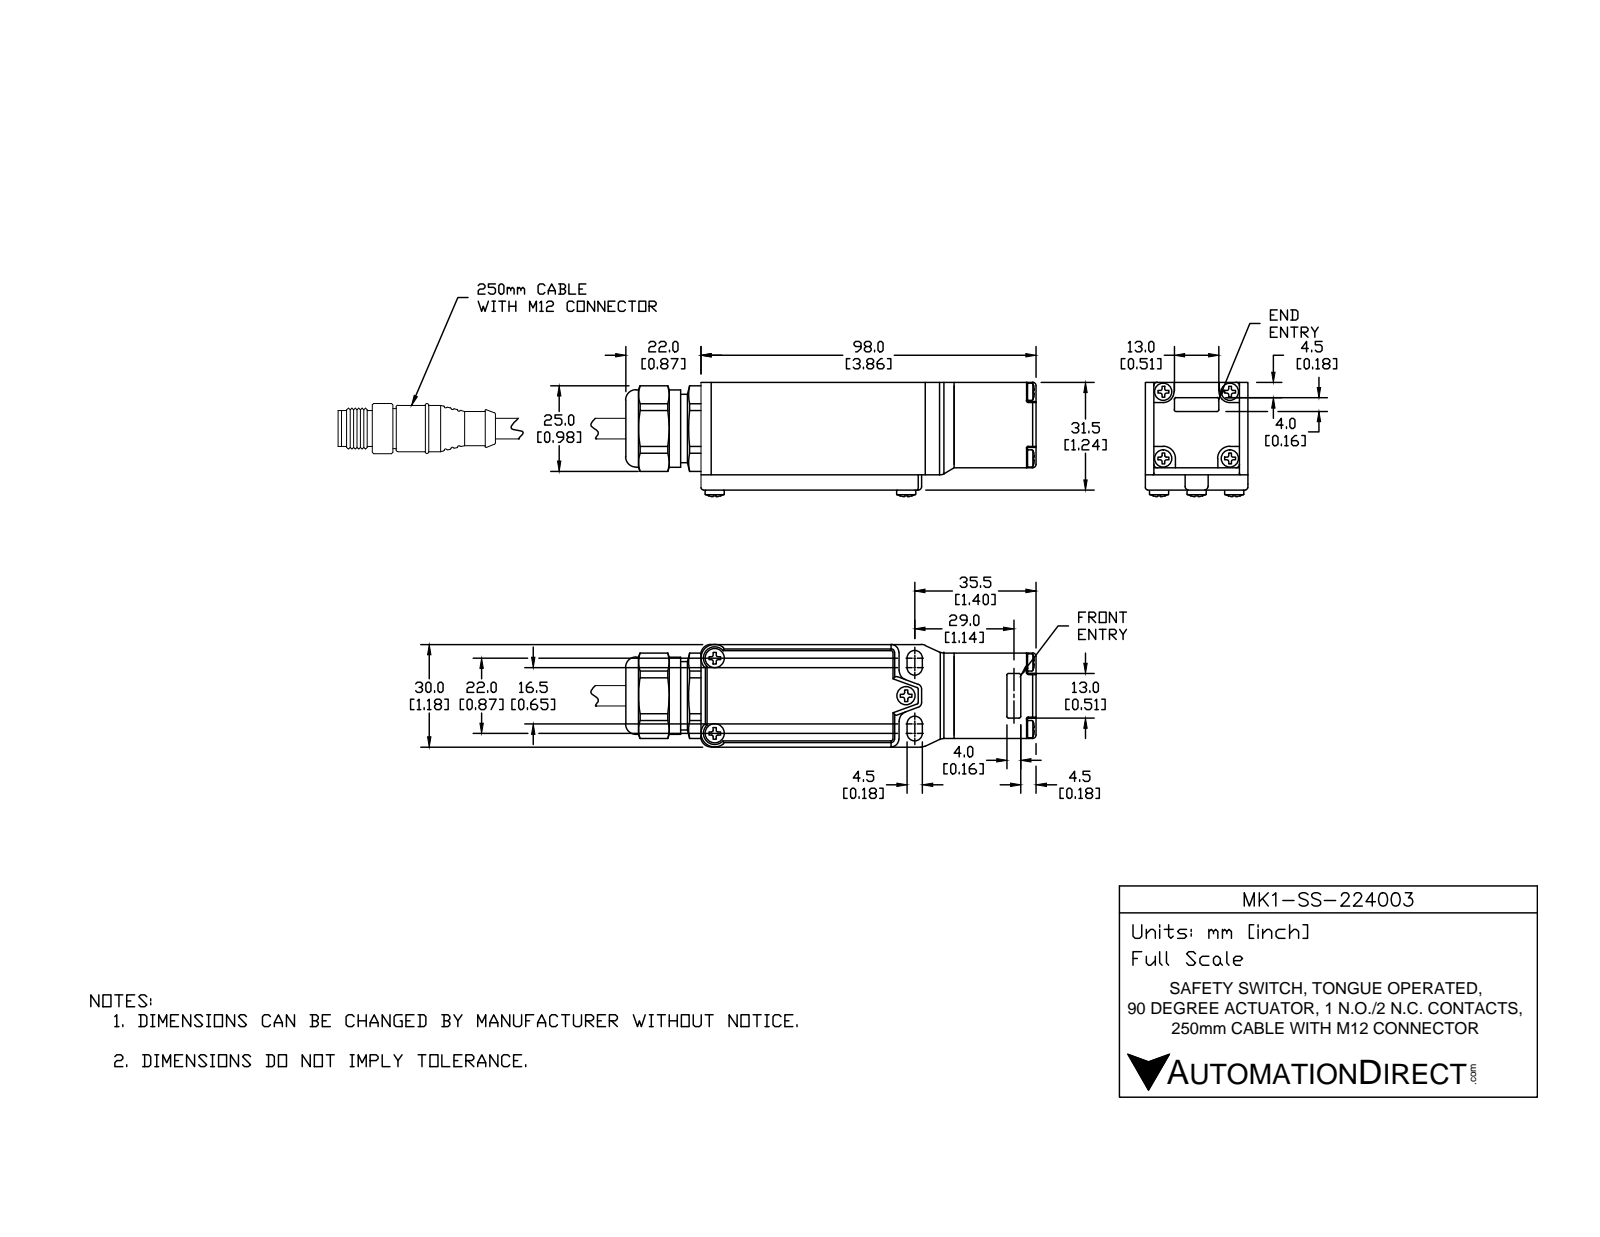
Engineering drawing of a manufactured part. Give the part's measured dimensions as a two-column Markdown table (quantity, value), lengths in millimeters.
| quantity | value |
| --- | --- |
| part name | MK1-SS-224003 |
| STEP written by | SolidWorks 2014 (AUTOMOTIVE_DESIGN) |
| units | millimeters |
| bodies | 12 solids, 1178 faces (346 planar, 474 cylindrical, 358 other) |
| overall size | 99 × 33.5 × 30 |
| volume | 37 330 mm³ |
| surface area | 31 410 mm² |
| round holes (diameter × count) | 2.5 × 8, 3.2 × 7, 4 × 3, 1.5 × 2, 1.8 × 2, 2.2 × 2, 3.6 × 2, 2.9 × 1, 4.4 × 1, 5.5 × 1, 10.3 × 1, 13.6 × 1 |
| round bosses / shafts (diameter × count) | 3 × 7, 5 × 5, 3.5 × 4, 5.6 × 3, 23.5 × 1, 17.7 × 1, 6 × 1 |
| partial cylindrical surfaces (radius × count) | 0.5 × 159, 0.3 × 58, 1 × 24, 0.2 × 14, 0.7 × 8, 0.8 × 8, 3 × 8, 2.3 × 4 |
| main face-to-face distances | 2.5, 2, 29, 2.9, 27.1, 30, 31.5, 4.5, 1, 24.6 |
| hole center spacings | 13.8, 19.5, 4.7, 10.7, 10.8, 12.1, 12.8, 14.8 |
